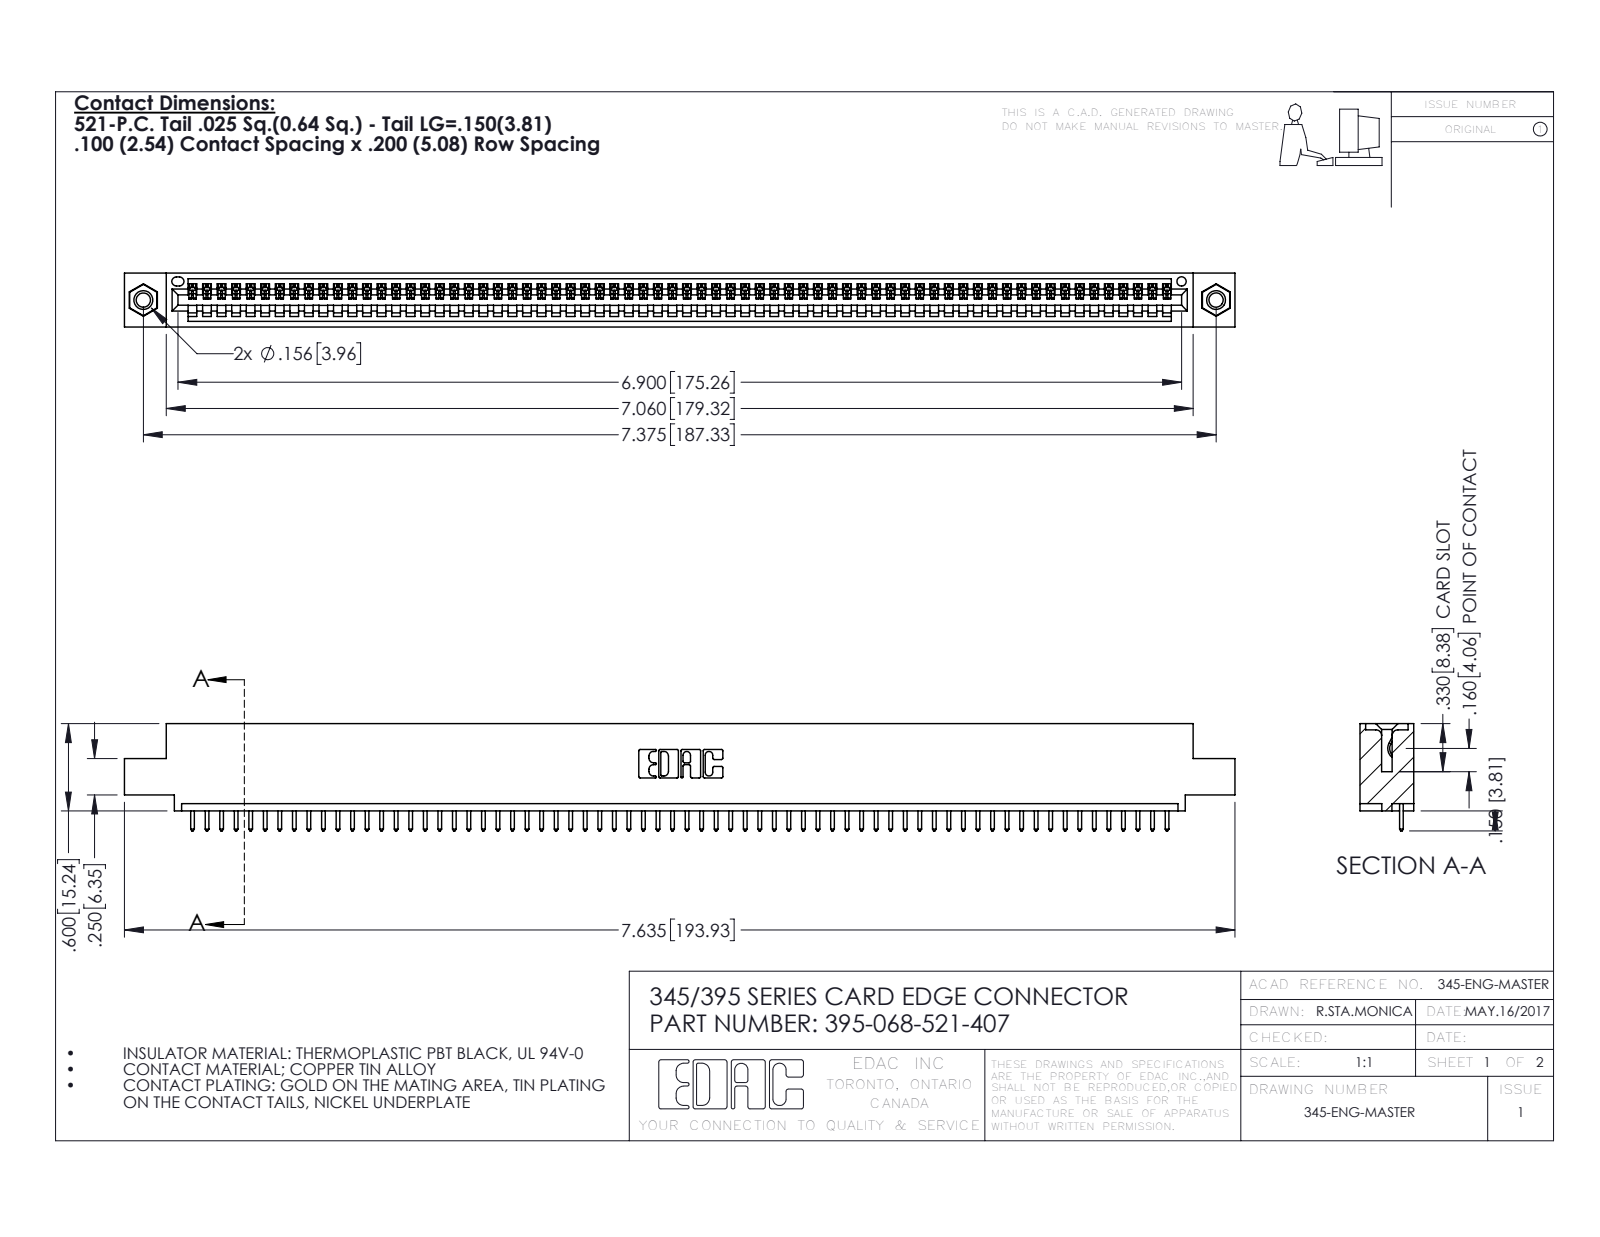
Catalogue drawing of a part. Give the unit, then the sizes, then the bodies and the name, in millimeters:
Units: millimetres
Overall size (bounding box): 193.9 × 18.7 × 9.4
Round holes (diameter × count): ⌀2.5 ×2, ⌀3.2 ×2, ⌀4 ×2, ⌀1.6 ×1
Round bosses / shafts (diameter × count): ⌀3.9 ×2
Partial cylindrical surfaces — rounded edges, fillets, slot ends (radius × count): R0.2 ×136, R0.3 ×136, R0.3 ×22, R0.2 ×6, R0.8 ×6, R0.7 ×3, R0.8 ×2, R1 ×2
Main face-to-face distances: 1.8, 7.6, 9.4, 5.1, 2.5, 6.9, 0.6, 5.7, 3.8, 1.8
Hole centre spacings: 6.9, 181.3, 187.3
Volume: 18 350 mm³ · Surface area: 24 100 mm²
Bodies: 71 solids, 4134 faces (2836 planar, 1282 cylindrical, 16 other)
Part name (STEP PRODUCT): 395-068-521-407; 345 Part_0.110 Offset - 0.156 Dia-TI; 345-292-001_345-293-121; 345-250-001_345-250-005-103
STEP written by: SolidWorks 2016 (CONFIG_CONTROL_DESIGN)
